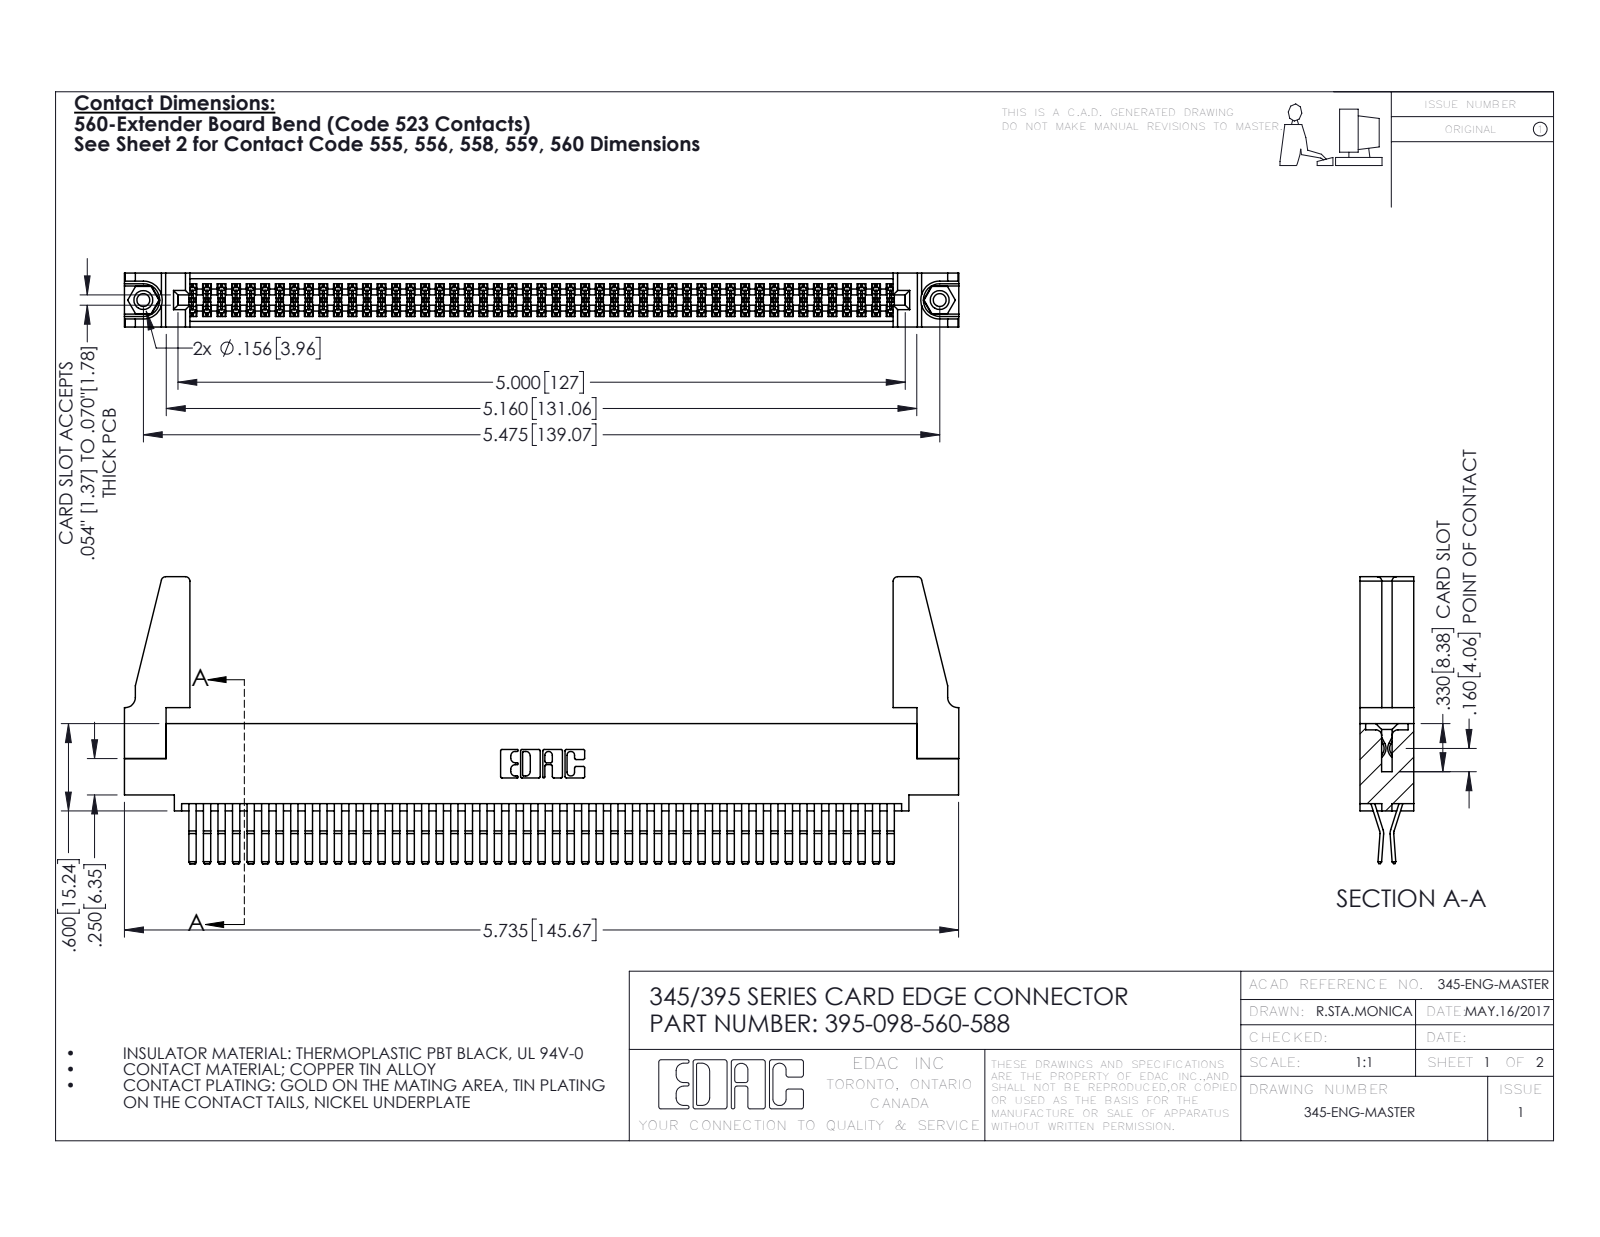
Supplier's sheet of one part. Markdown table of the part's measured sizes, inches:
| quantity | value |
| --- | --- |
| part name | 345-292-001_560 Tail; 345 Part_0.110 Offset - 0.156 Dia-TH; 345-220-078_345-220-088; 395-098-560-588 (+1 more) |
| STEP written by | SolidWorks 2016 (CONFIG_CONTROL_DESIGN) |
| units | inches |
| bodies | 103 solids, 5350 faces (3390 planar, 1944 cylindrical, 16 other) |
| overall size | 5.736 × 1.972 × 0.37 |
| volume | 1.101 in³ |
| surface area | 41.63 in² |
| round holes (diameter × count) | 0.089 × 2, 0.125 × 2, 0.156 × 2, 0.064 × 1 |
| round bosses / shafts (diameter × count) | 0.155 × 2 |
| partial cylindrical surfaces (radius × count) | 0.006 × 147, 0.01 × 22, 0.03 × 8, 0.007 × 6, 0.031 × 6, 0.026 × 3, 0.01 × 2, 0.014 × 2 |
| main face-to-face distances | 0.072, 0.298, 0.025, 0.37, 0.2, 0.098, 0.272, 0.225, 0.175, 0.149 |
| hole center spacings | 0.27, 5.239, 5.475 |
